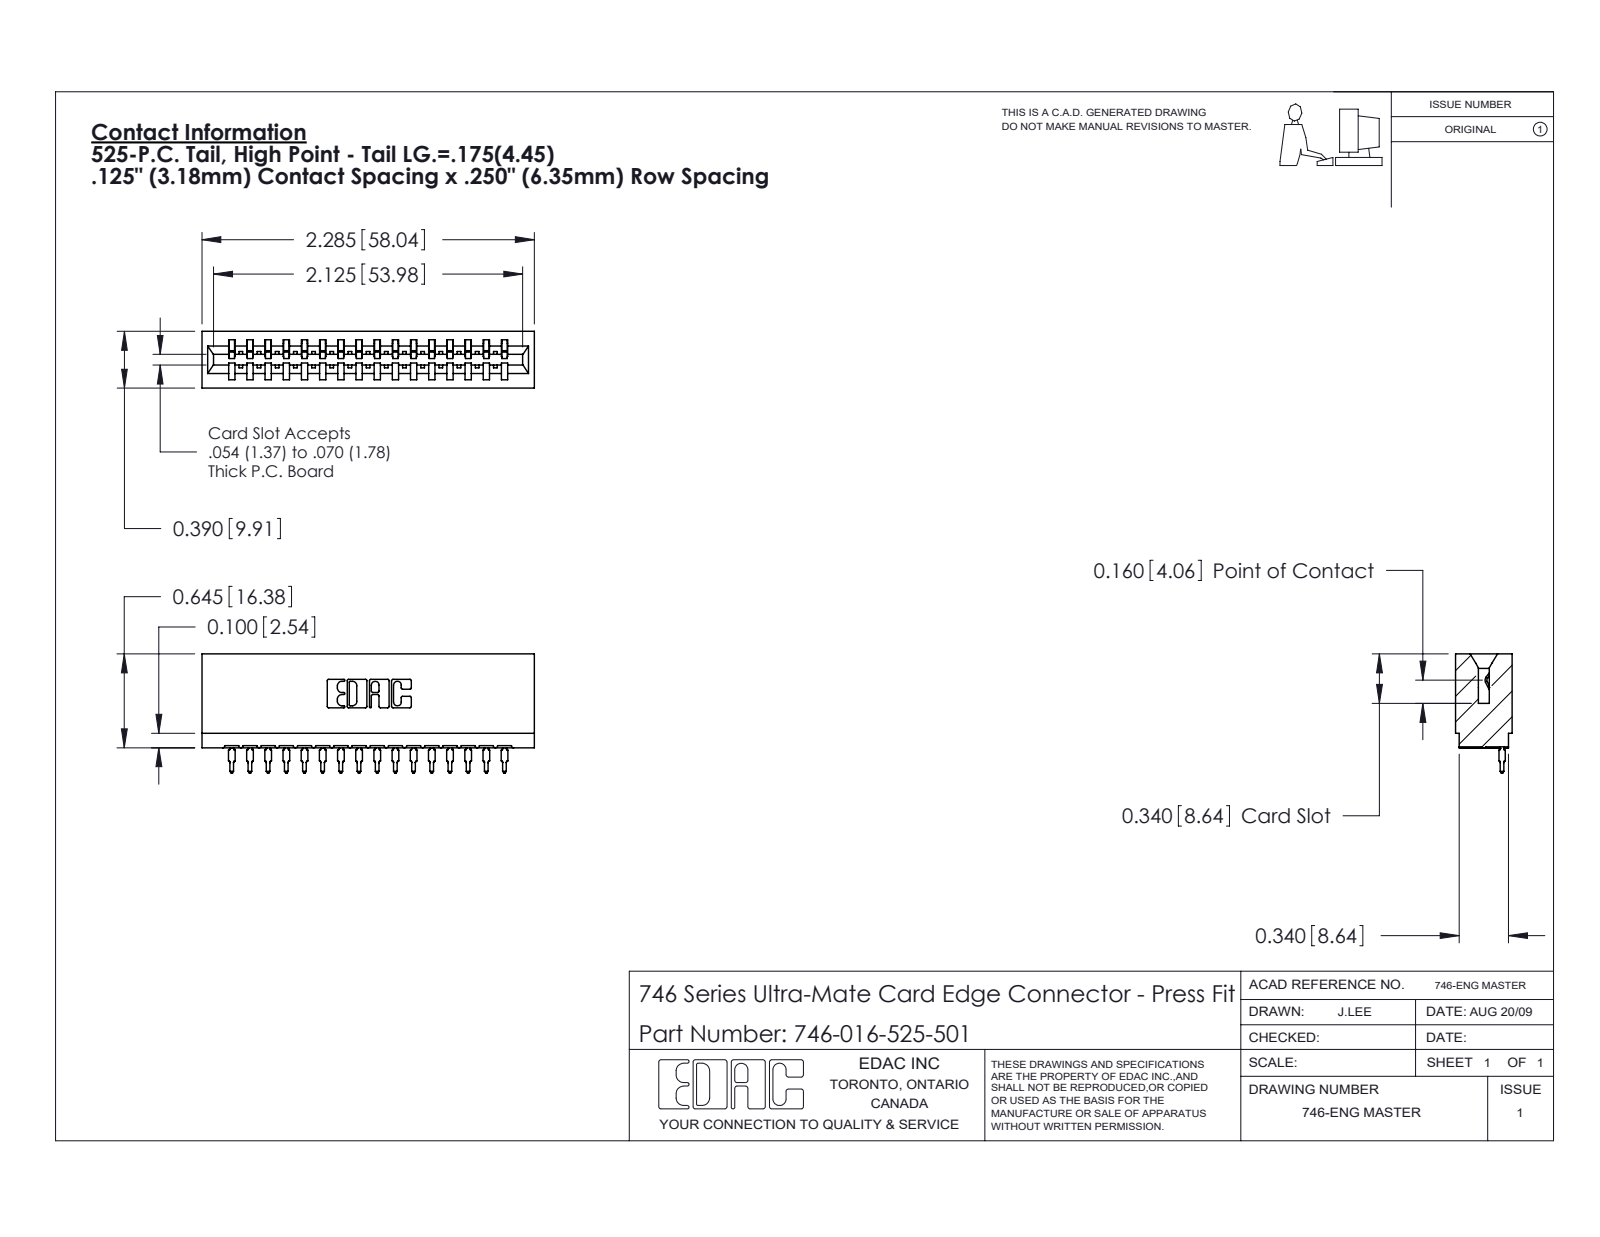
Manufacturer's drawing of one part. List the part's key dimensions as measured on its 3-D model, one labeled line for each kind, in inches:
Part name (STEP PRODUCT): 746-292-001_525; 746-016-525-501; 746 Part_.340 Slot Depth - 01
STEP written by: SolidWorks 2020 (CONFIG_CONTROL_DESIGN)
Units: inches
Bodies: 17 solids, 1825 faces (1063 planar, 346 cylindrical, 416 other)
Overall size (bounding box): 2.285 × 0.819 × 0.39
Volume: 0.406 in³ · Surface area: 13.17 in²
Partial cylindrical surfaces — rounded edges, fillets, slot ends (radius × count): R0.021 ×32, R0.01 ×22, R0.015 ×17, R0.007 ×6, R0.031 ×6, R0.005 ×4, R0.011 ×4, R0.026 ×3
Main face-to-face distances: 0.25, 0.057, 0.333, 0.5, 0.39, 0.125, 0.125, 0.292, 0.542, 0.042
